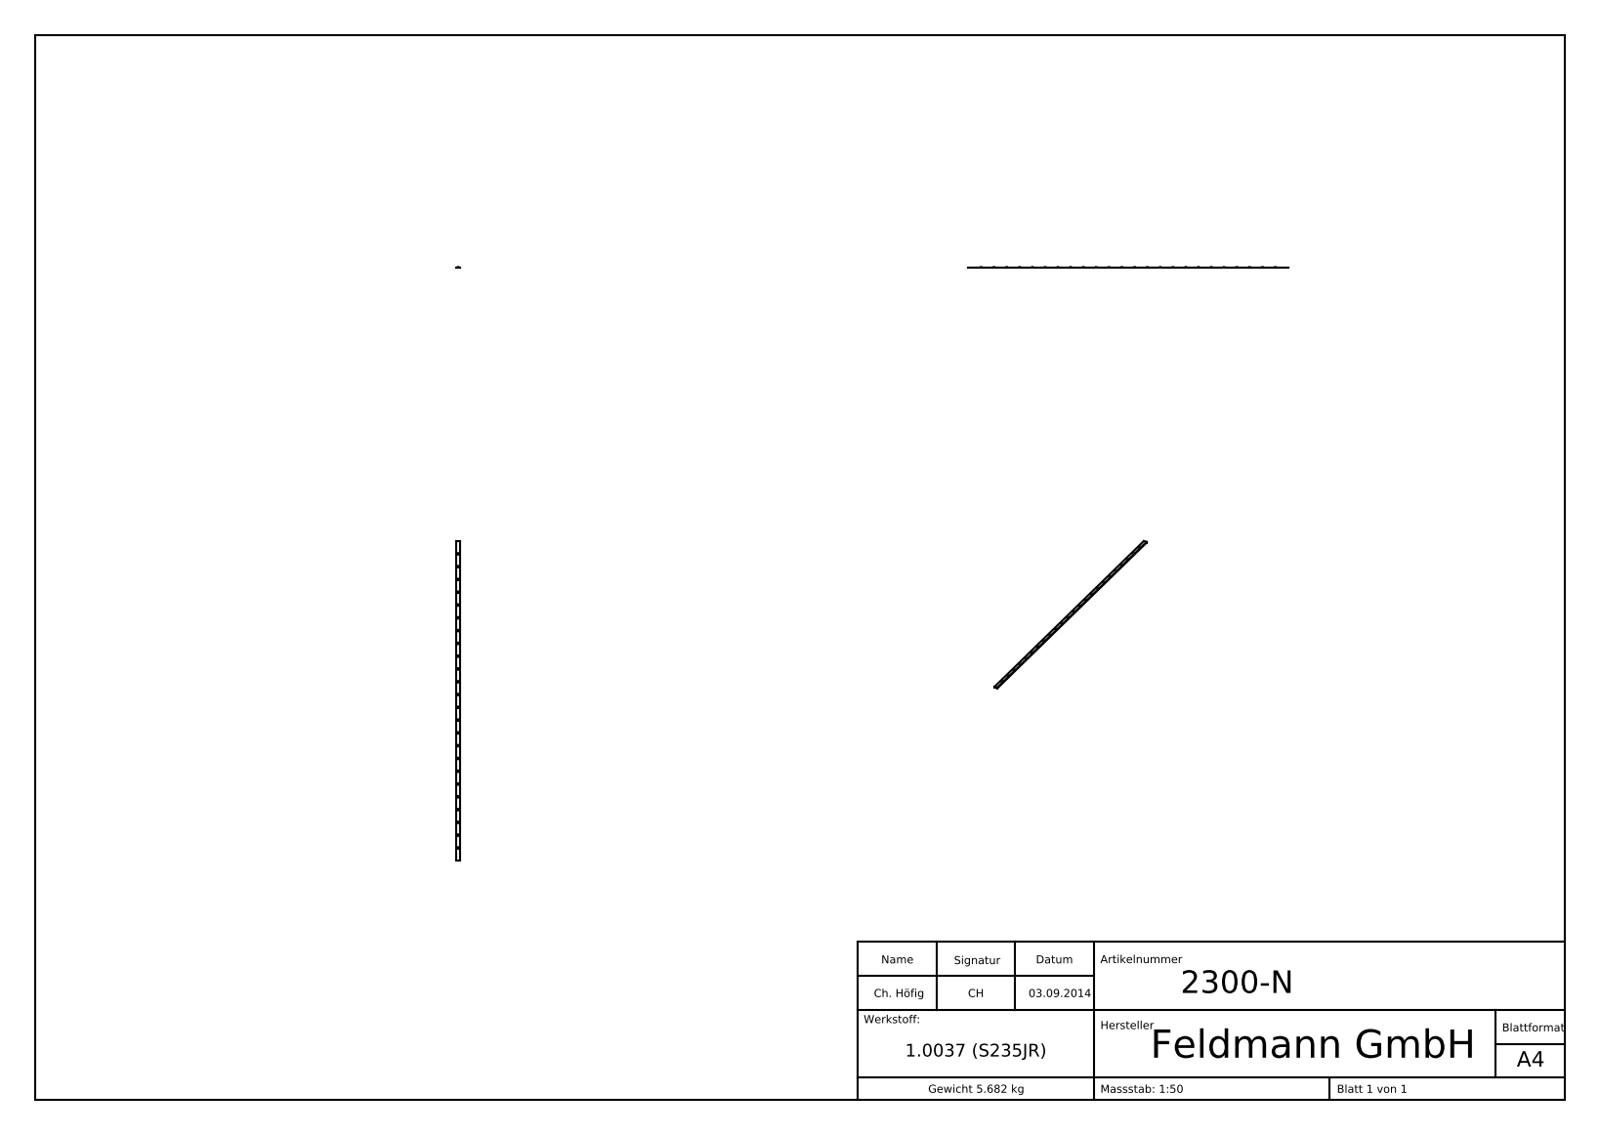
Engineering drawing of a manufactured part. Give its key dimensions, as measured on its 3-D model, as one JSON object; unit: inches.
{"part_name": "2300-N", "step_written_by": "SolidWorks 2015 (CONFIG_CONTROL_DESIGN)", "units": "inches", "bodies": {"solids": 1, "faces": 167, "planar": 71, "cylindrical": 0, "other": 96}, "overall_size": [118.11, 1.181, 0.472], "volume_in3": 44.46, "surface_area_in2": 355.8, "face_to_face_distances": [0.315, 1.181, 118.11, 0.02, 118.091, 0.015, 0.117, 0.157, 0.044, 0.161]}
